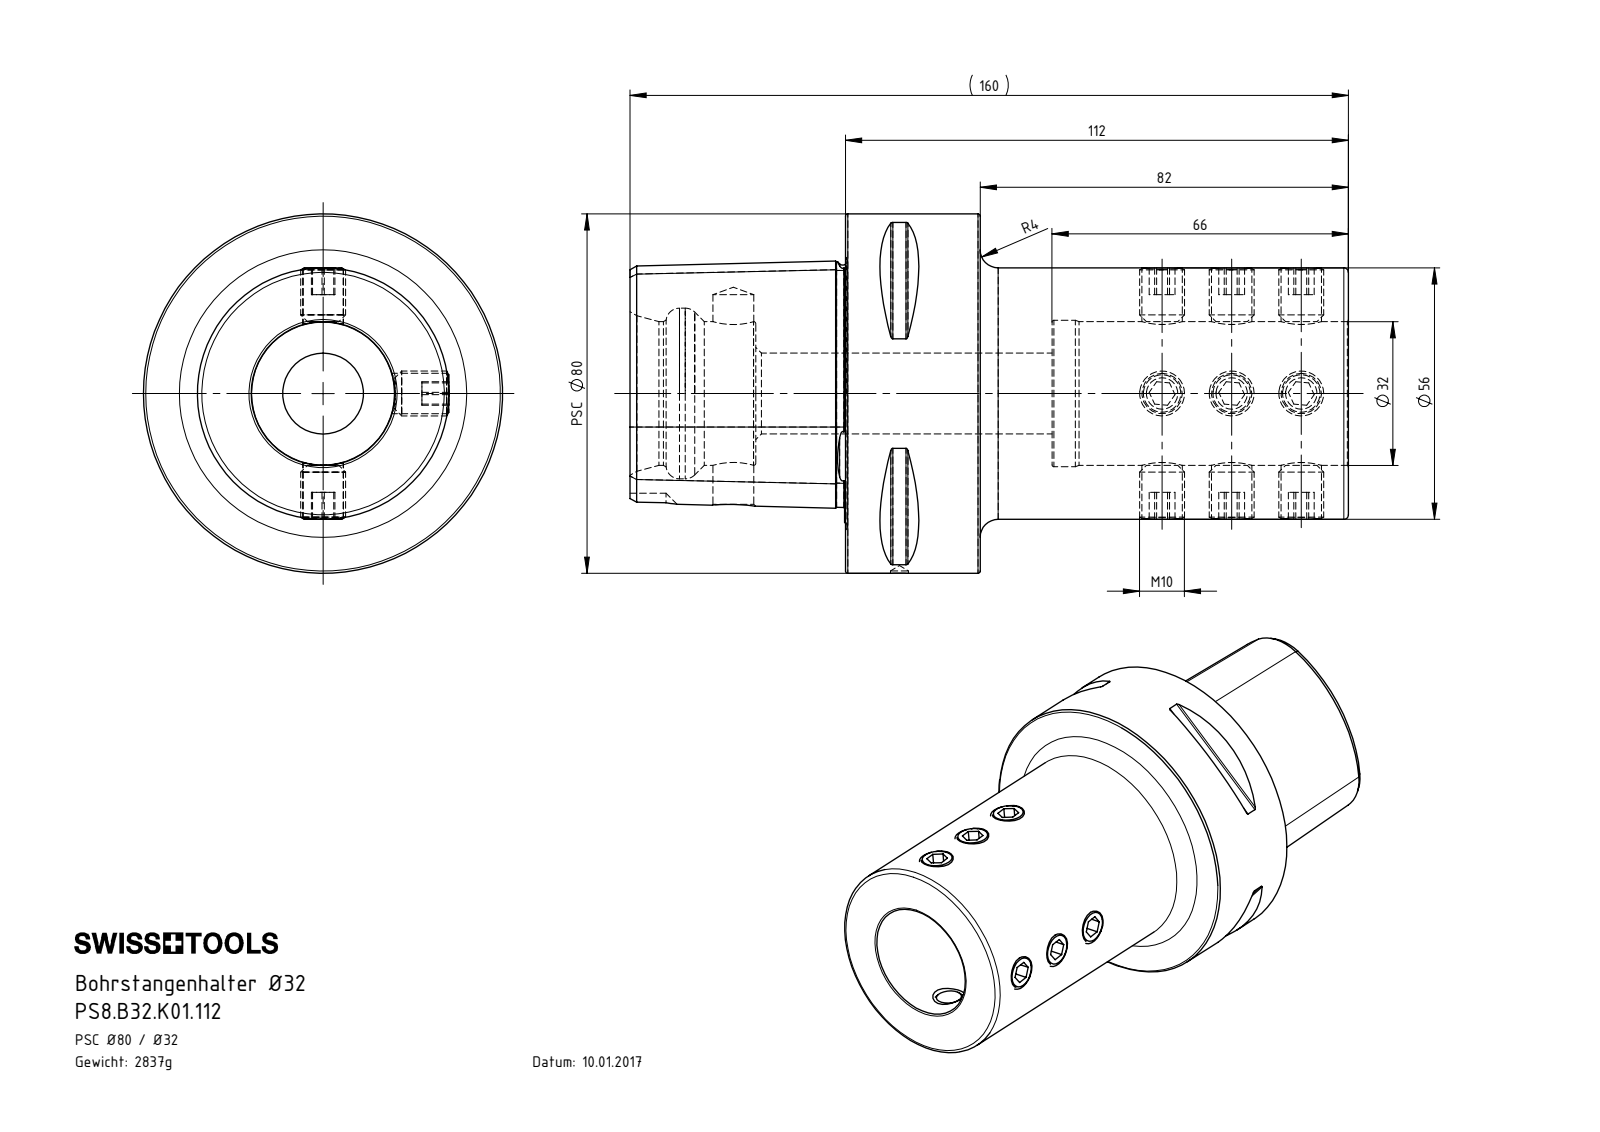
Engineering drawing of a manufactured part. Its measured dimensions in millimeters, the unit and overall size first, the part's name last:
Units: millimetres
Overall size (bounding box): 160 × 80 × 80
Round holes (diameter × count): ⌀9 ×6, ⌀4 ×1, ⌀9.1 ×1, ⌀18 ×1, ⌀32 ×1, ⌀32.6 ×1, ⌀38 ×1
Round bosses / shafts (diameter × count): ⌀10 ×6, ⌀80 ×1, ⌀56 ×1
Partial cylindrical surfaces — rounded edges, fillets, slot ends (radius × count): R0.5 ×8, R6 ×1
Main face-to-face distances: 30, 112, 82, 66, 48, 78, 160, 50, 94, 46
Hole centre spacings: 15.5, 31, 37, 58.5, 74, 89.5, 95.5, 111
Volume: 361 407 mm³ · Surface area: 60 428 mm²
Bodies: 10 solids, 292 faces (102 planar, 67 cylindrical, 123 other)
Part name (STEP PRODUCT): PS8.B32.K01.112; PS8-B32.K01.112_A; ISO 4026 - M10 x 12_PreviewCfg
STEP written by: SolidWorks 2015 (AUTOMOTIVE_DESIGN)
